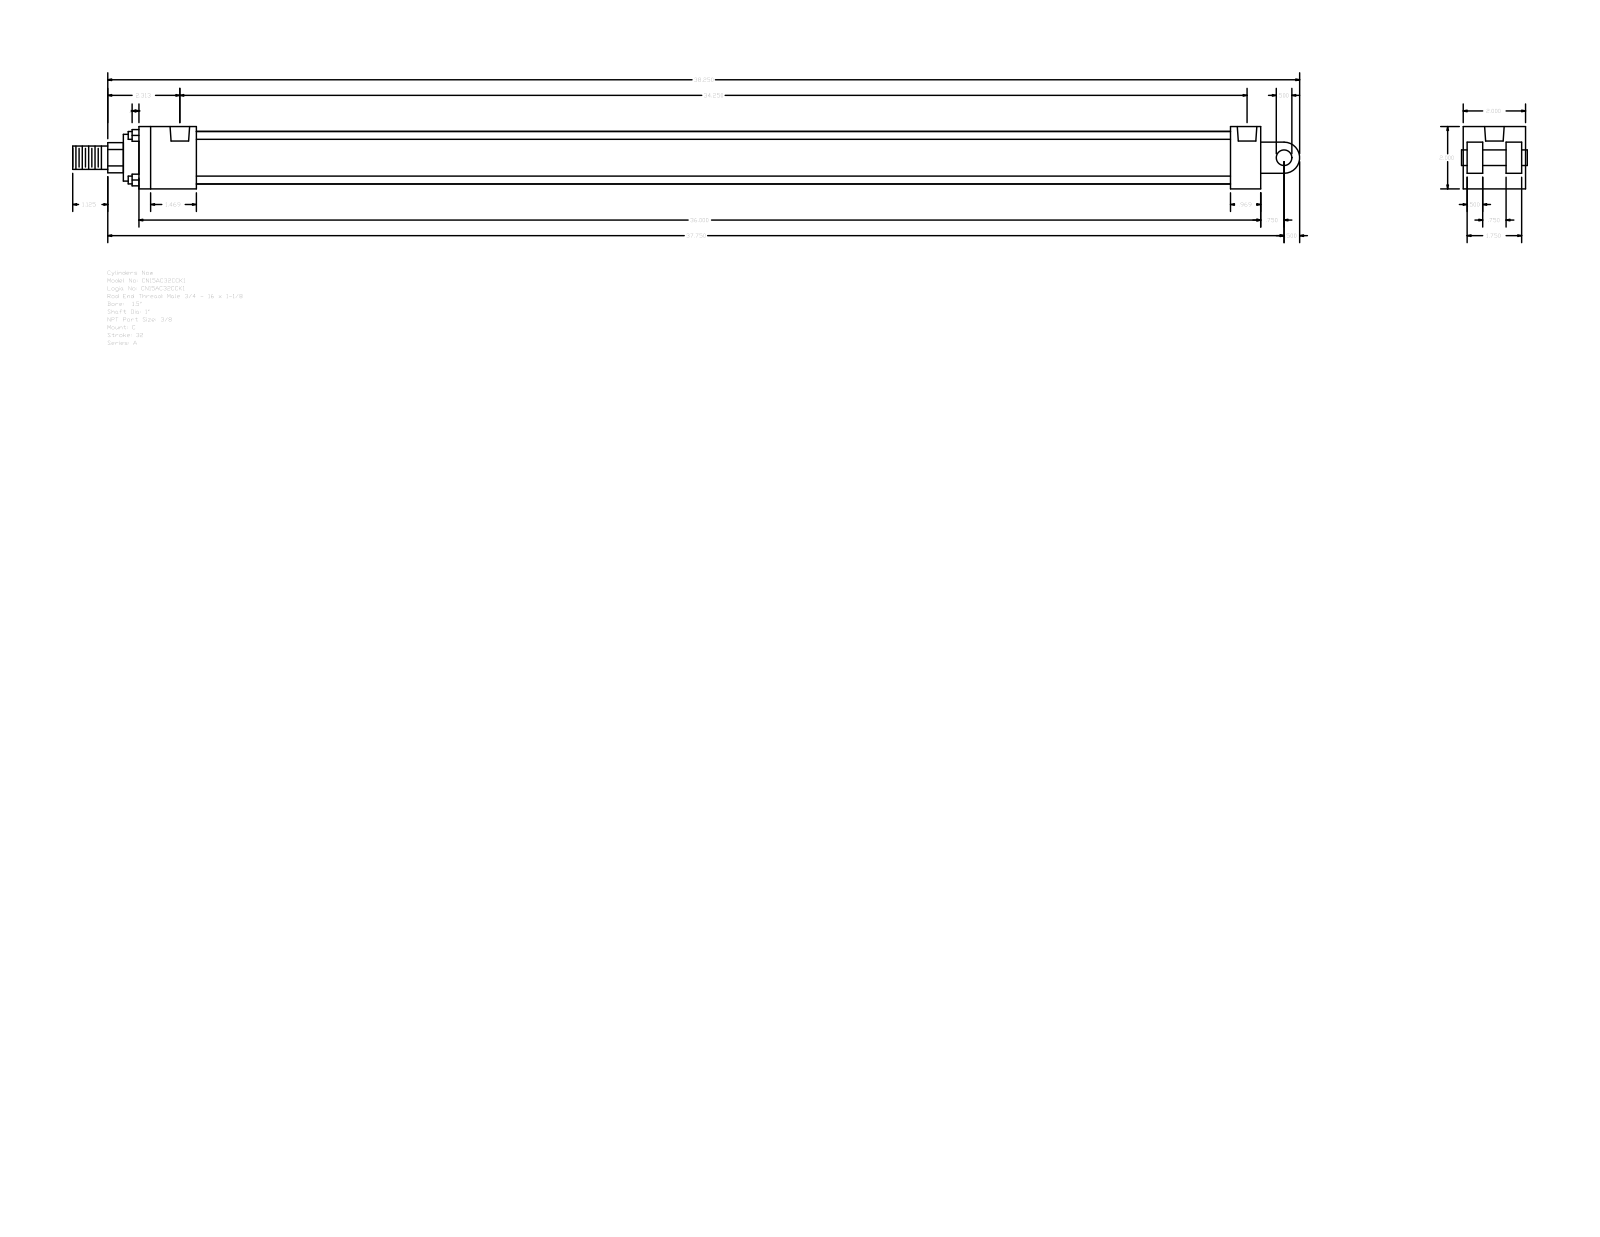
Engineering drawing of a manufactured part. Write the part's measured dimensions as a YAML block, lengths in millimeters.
part_name: "A_C__0150_1"
step_written_by: "GSSL Pune (CONFIG_CONTROL_DESIGN)"
units: millimeters
bodies: {solids: 0, faces: 99, planar: 70, cylindrical: 29, other: 0}
overall_size: [1000.12, 50.8, 50.8]
round_holes:
  - {diameter: 5.56, count: 4}
  - {diameter: 15.93, count: 2}
round_bosses_or_shafts:
  - {diameter: 6.35, count: 4}
  - {diameter: 42.93, count: 1}
  - {diameter: 38.1, count: 1}
  - {diameter: 25.4, count: 1}
  - {diameter: 19.05, count: 1}
  - {diameter: 12.7, count: 1}
partial_cylinders:
  - {radius: 12.29, count: 1}
  - {radius: 12.7, count: 1}
face_to_face_distances: [50.8, 12.7, 3.17, 15.87, 47.63, 34.93, 31.76, 914.4, 38.1, 889.79]
hole_center_spacings: [3.97, 862.01, 865.98, 869.95]
